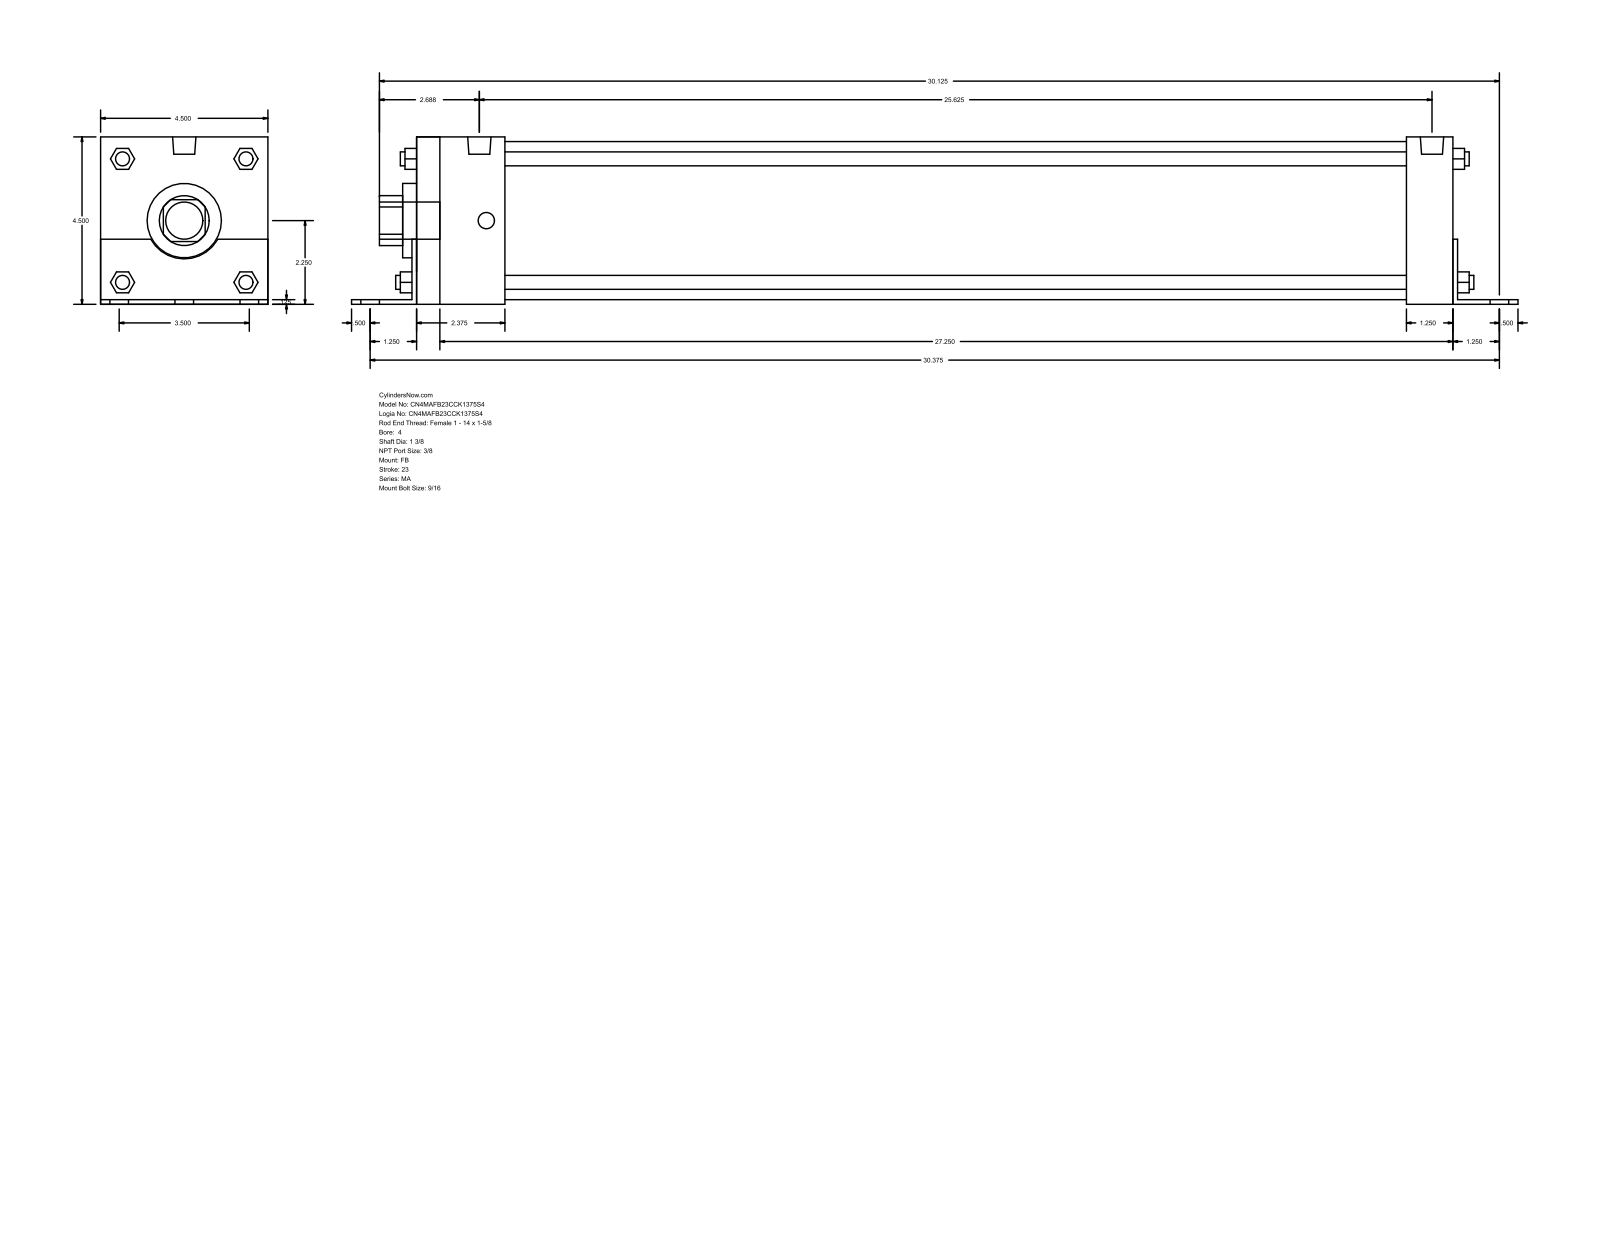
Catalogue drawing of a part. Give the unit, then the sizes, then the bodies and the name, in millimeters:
Units: millimetres
Overall size (bounding box): 796.92 × 114.35 × 114.3
Round holes (diameter × count): ⌀34.92 ×1, ⌀50.8 ×1, ⌀107.95 ×1
Round bosses / shafts (diameter × count): ⌀14.29 ×6, ⌀11.11 ×4, ⌀9.53 ×4, ⌀15.93 ×2, ⌀25.4 ×1
Partial cylindrical surfaces — rounded edges, fillets, slot ends (radius × count): R17.06 ×1, R26.16 ×1
Main face-to-face distances: 114.3, 3.17, 114.35, 3.12, 111.18, 708.02, 3.18, 711.2, 34.93, 60.32
Bodies: 0 solids, 140 faces (105 planar, 35 cylindrical, 0 other)
Part name (STEP PRODUCT): MA_FB__0400_1.375
STEP written by: GSSL Pune (CONFIG_CONTROL_DESIGN)
